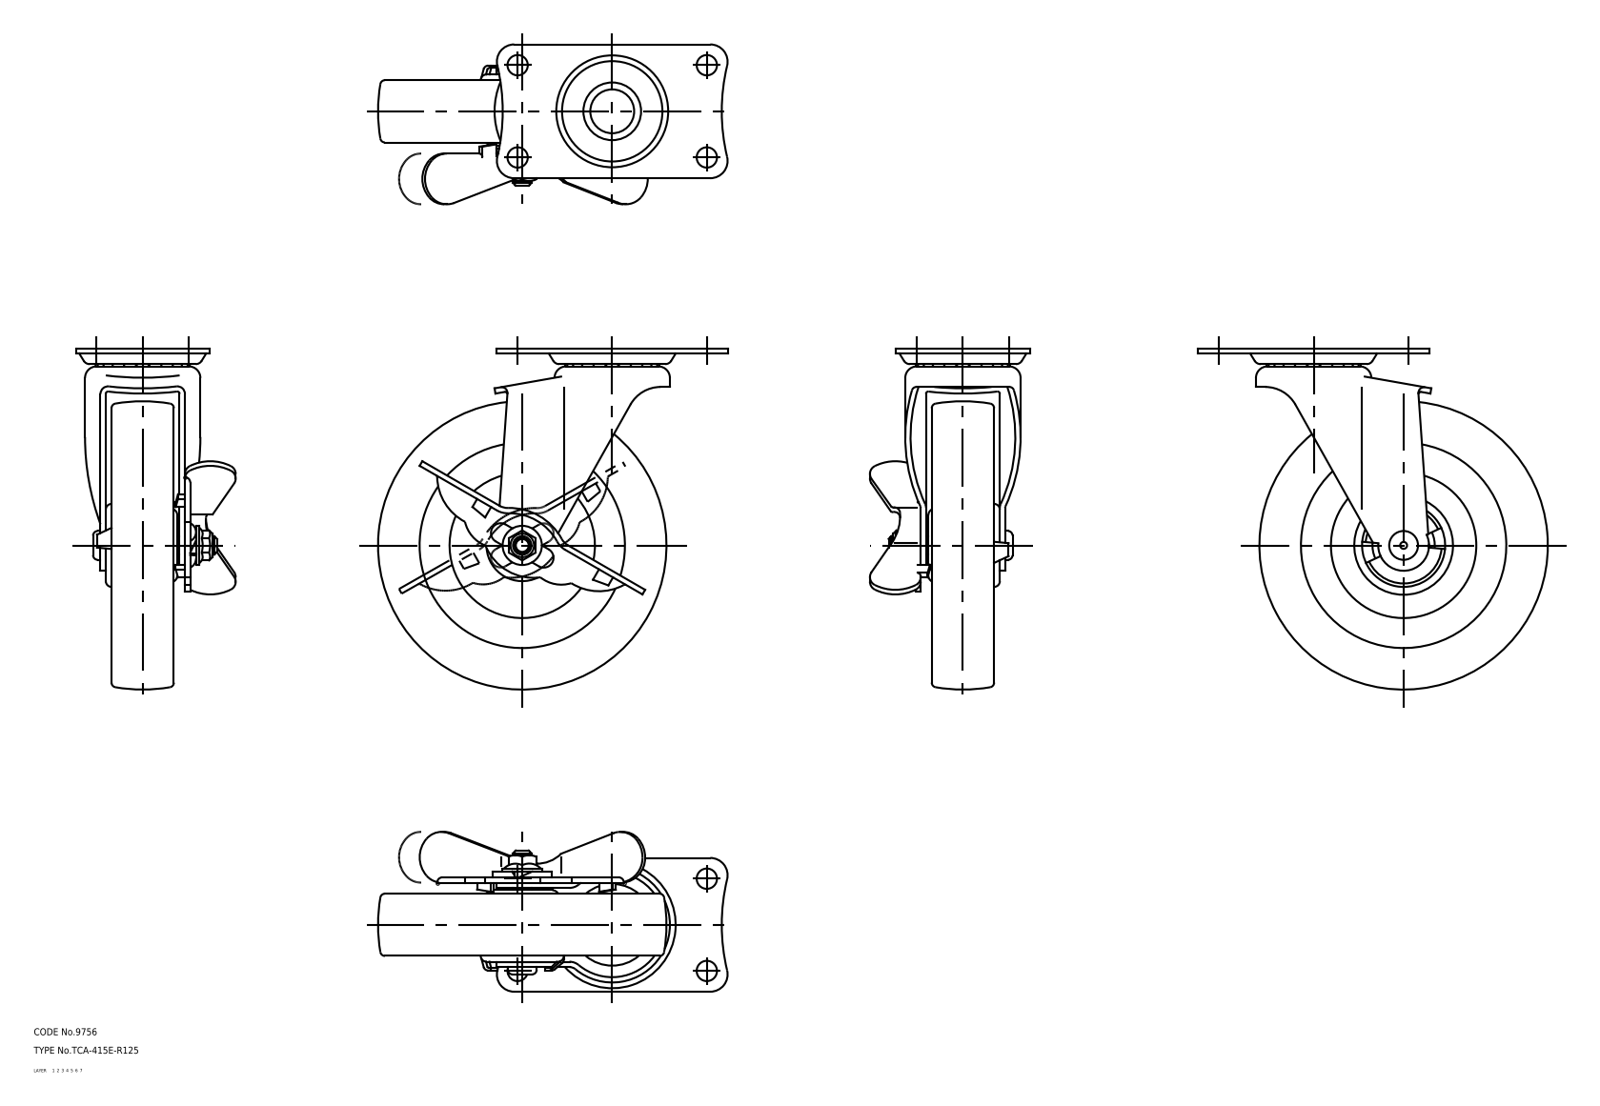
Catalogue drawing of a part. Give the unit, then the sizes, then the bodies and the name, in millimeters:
Units: millimetres
Overall size (bounding box): 151.5 × 148 × 69.3
Volume: 372 991 mm³ · Surface area: 82 245 mm²
Bodies: 6 solids, 349 faces (0 planar, 0 cylindrical, 349 other)
Part name (STEP PRODUCT): wheel; mounting plate; main shaft; lever (+2 more)
STEP written by: CADfix (AUTOMOTIVE_DESIGN)
